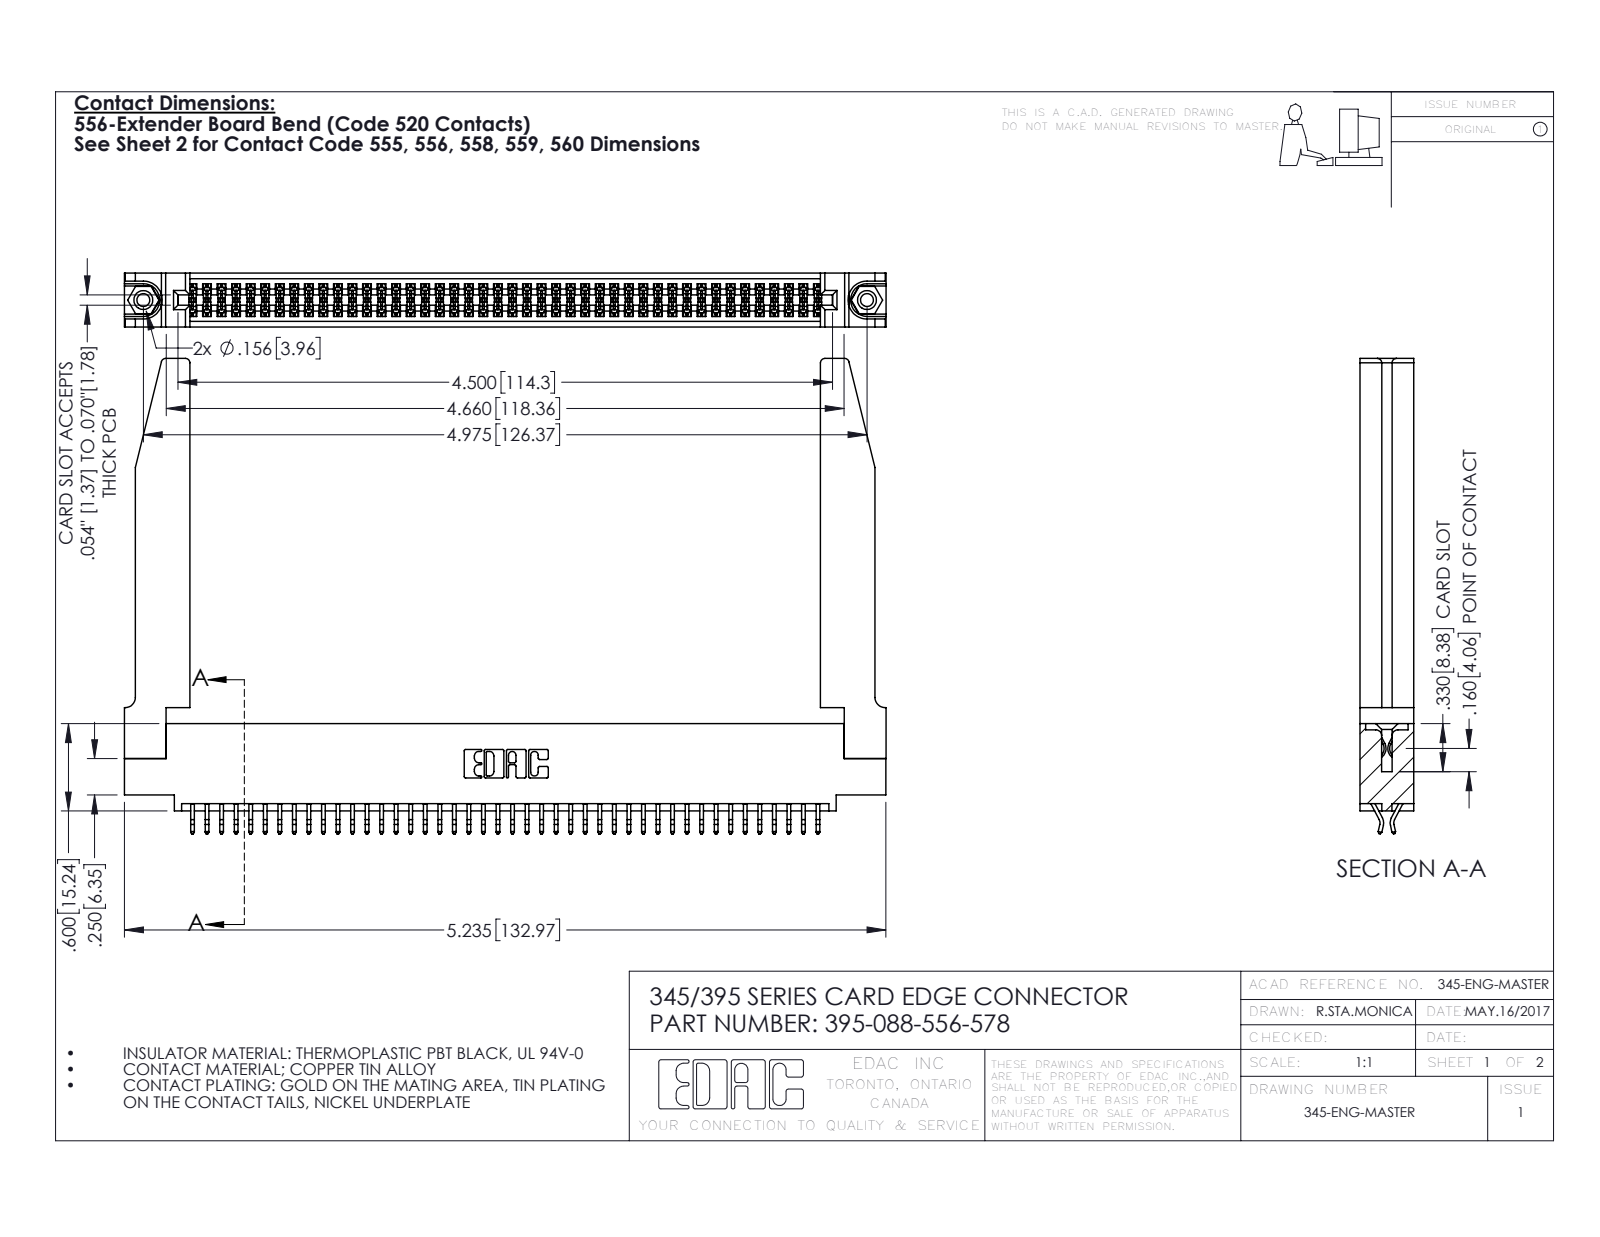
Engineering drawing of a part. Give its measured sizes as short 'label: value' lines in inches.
name: 345-292-001_556 Tail; 395-088-556-578; 345-220-078_345-220-078; 345 Part_0.110 Offset - 0.156 Dia-TH (+1 more)
written by: SolidWorks 2016 (CONFIG_CONTROL_DESIGN)
unit: in
bodies: 93 solids, 5292 faces (3482 planar, 1758 cylindrical, 52 other)
size: 5.236 × 3.267 × 0.37
volume: 1.259 in³; area: 40.15 in²
holes: 2× ⌀0.089, 2× ⌀0.125, 2× ⌀0.156, 1× ⌀0.064
bosses: 2× ⌀0.155
rounds: 132× R0.006, 22× R0.01, 8× R0.03, 6× R0.007, 6× R0.031, 3× R0.026, 2× R0.01, 2× R0.014
face distances: 0.37, 0.072, 0.298, 0.025, 0.2, 0.098, 0.272, 0.225, 0.148, 0.15
hole spacings: 0.27, 4.739, 4.975
